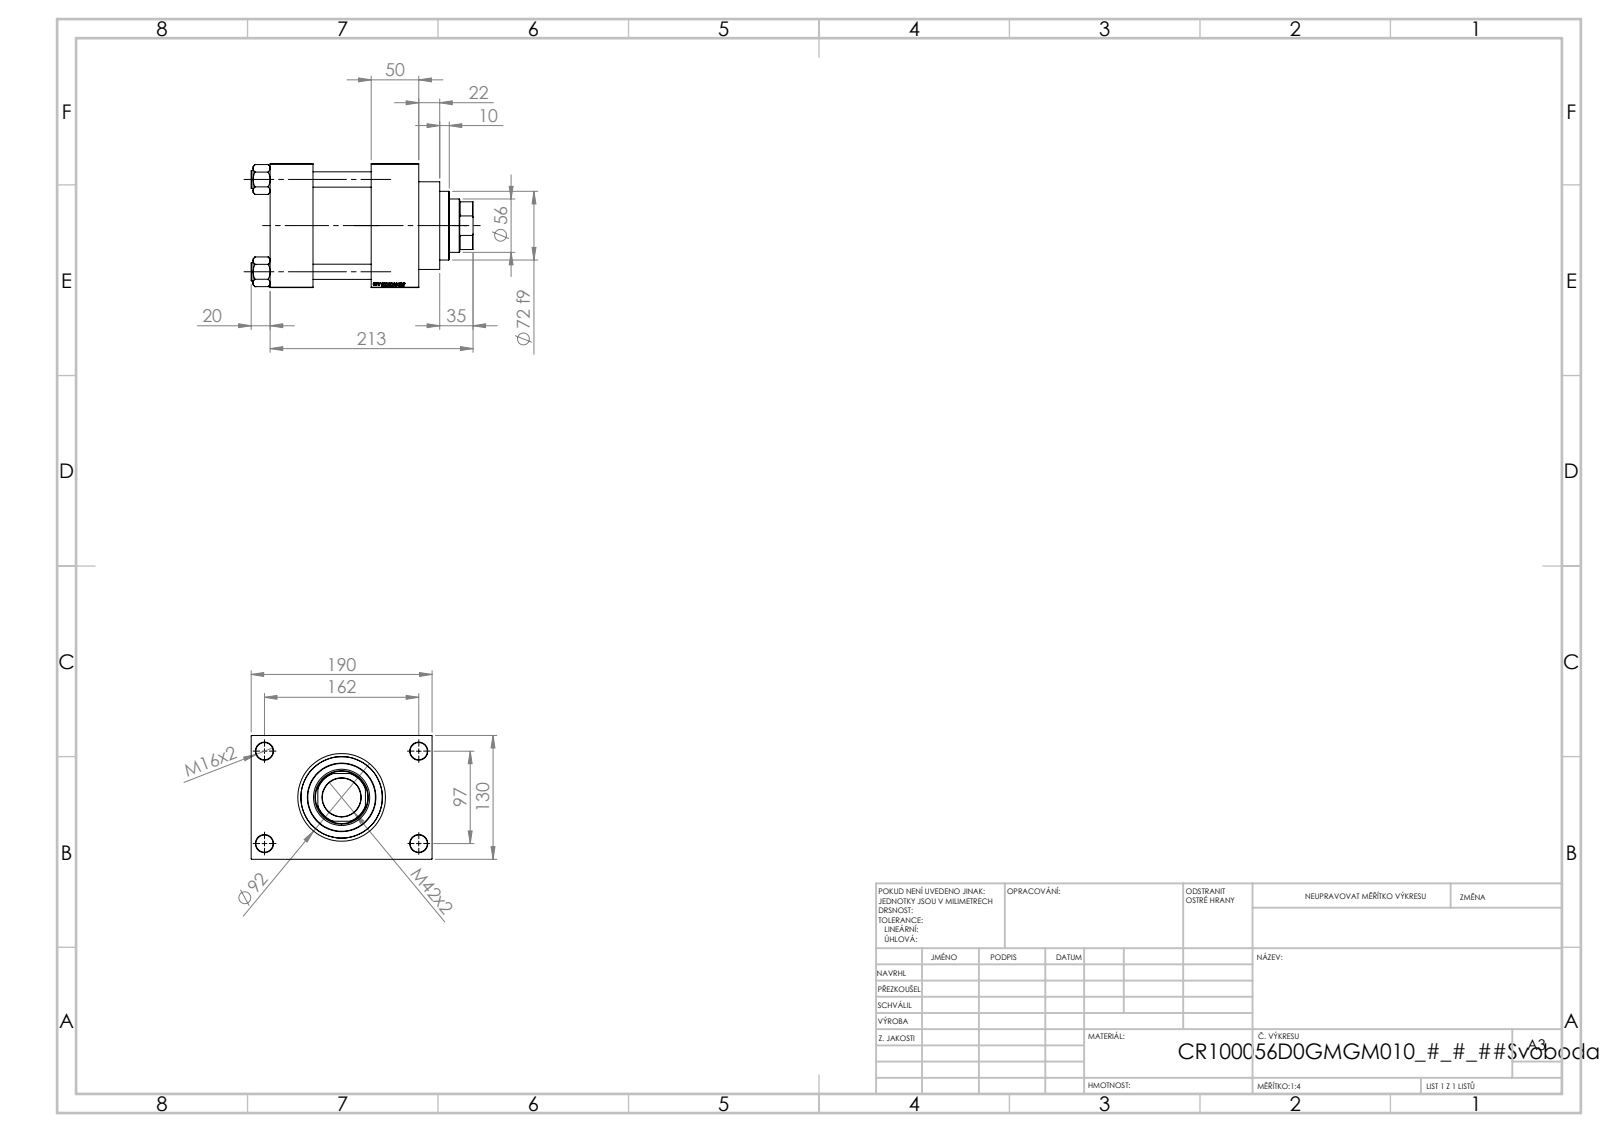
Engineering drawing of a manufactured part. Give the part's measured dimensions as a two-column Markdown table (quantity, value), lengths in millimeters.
| quantity | value |
| --- | --- |
| part name | V215CR_VCP_D; V215CR_D_Body; V215CR_D_TYCINKA; V215_VC_A (+1 more) |
| STEP written by | SolidWorks 2019 (CONFIG_CONTROL_DESIGN) |
| units | millimeters |
| bodies | 11 solids, 1151 faces (545 planar, 88 cylindrical, 518 other) |
| overall size | 233 × 190 × 130 |
| volume | 2 586 000 mm³ |
| surface area | 351 980 mm² |
| round holes (diameter × count) | 16 × 4, 18 × 4, 7 × 2, 26.44 × 2, 35 × 2, 40.5 × 1, 56 × 1, 59 × 1, 76 × 1, 85.5 × 1, 100 × 1 |
| round bosses / shafts (diameter × count) | 19 × 4, 106 × 1, 92 × 1, 72 × 1 |
| partial cylindrical surfaces (radius × count) | 27 × 1 |
| main face-to-face distances | 130, 50, 45, 106, 61, 156, 111, 30, 160, 10 |
| hole center spacings | 32.55, 68.52, 94.41, 96.9, 102.27, 129.45, 161.73, 97 |
